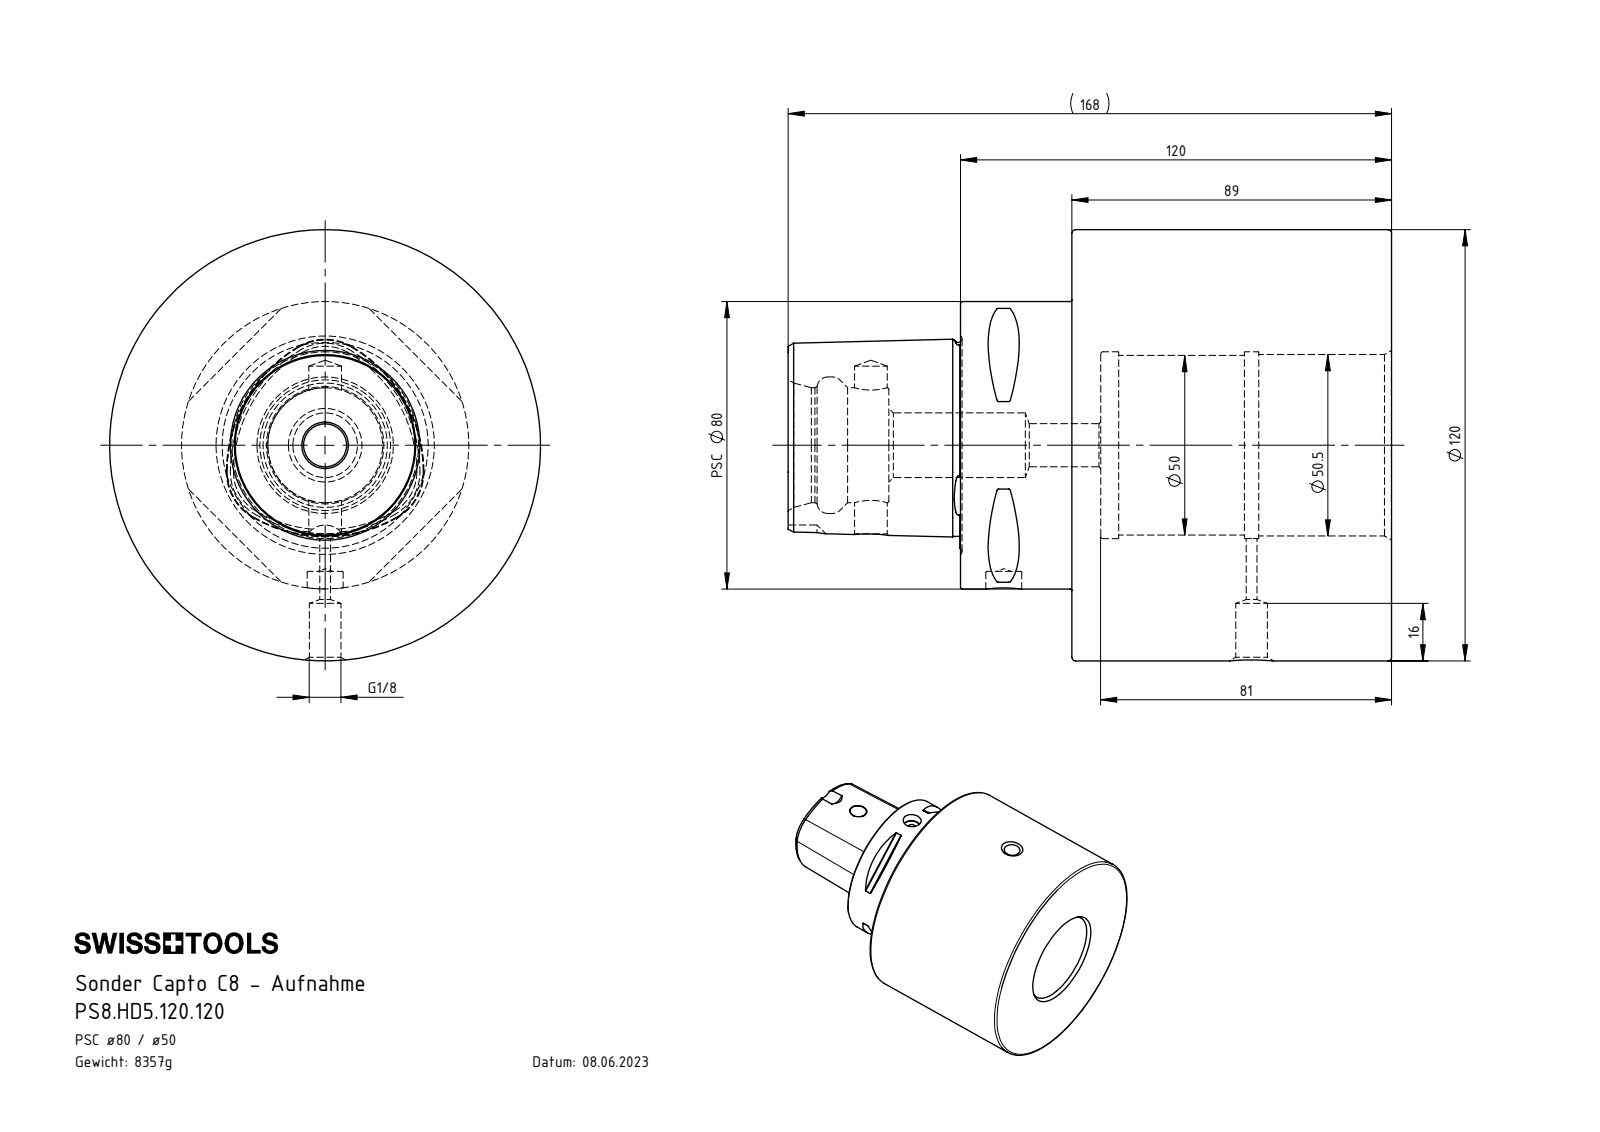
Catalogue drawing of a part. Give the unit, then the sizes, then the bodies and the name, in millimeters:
Units: millimetres
Overall size (bounding box): 168 × 120 × 120
Round holes (diameter × count): ⌀3 ×1, ⌀8.8 ×1, ⌀9.1 ×1, ⌀10 ×1, ⌀12 ×1, ⌀18 ×1, ⌀32 ×1, ⌀38 ×1, ⌀50 ×1, ⌀50.5 ×1, ⌀52 ×1
Round bosses / shafts (diameter × count): ⌀120 ×1, ⌀80 ×1
Partial cylindrical surfaces — rounded edges, fillets, slot ends (radius × count): R0.5 ×8, R6 ×1
Main face-to-face distances: 89, 31, 120, 39, 8, 81, 48, 79, 87, 168
Hole centre spacings: 37, 69, 106
Volume: 1 065 000 mm³ · Surface area: 91 812 mm²
Bodies: 1 solid, 167 faces (25 planar, 41 cylindrical, 101 other)
Part name (STEP PRODUCT): PS8-HD5.120.120_A; PS8.HD5.120.120
STEP written by: SolidWorks 2017 (AUTOMOTIVE_DESIGN)
